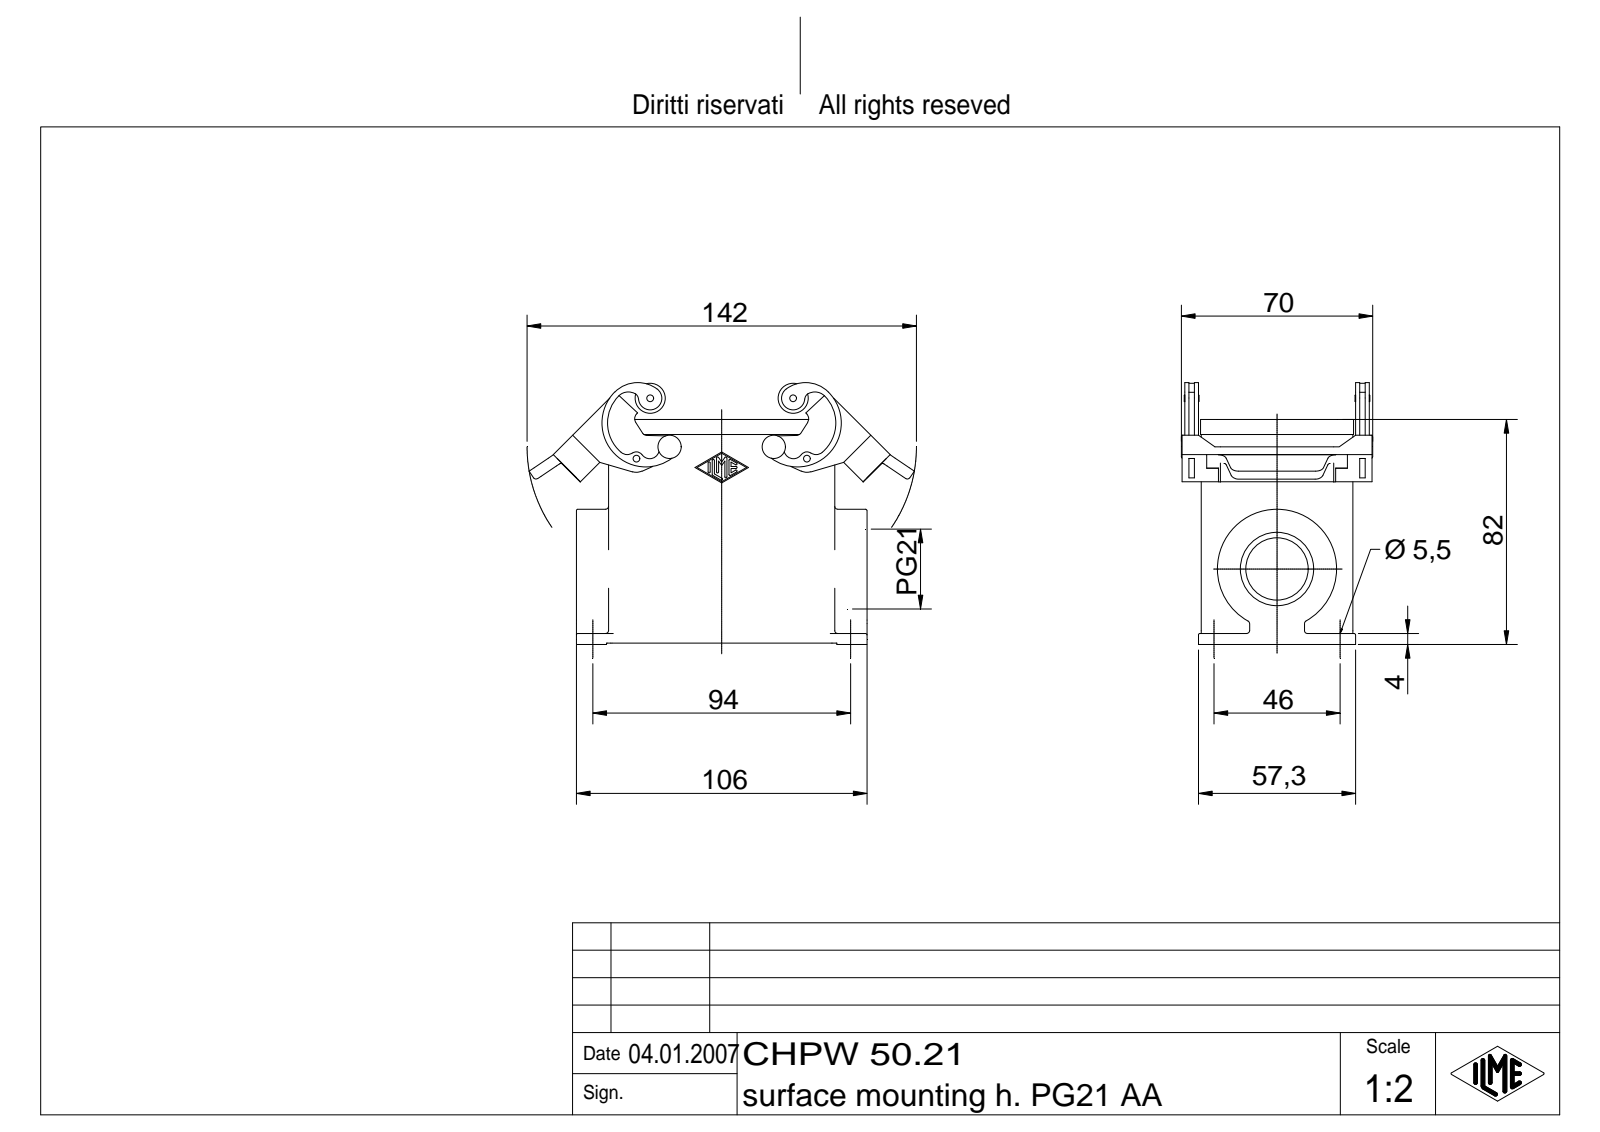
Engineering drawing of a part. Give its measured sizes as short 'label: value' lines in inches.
name: CHPW 50.21
written by: Autodesk Inventor 7 (AUTOMOTIVE_DESIGN)
unit: in
bodies: 1 solid, 911 faces (196 planar, 295 cylindrical, 420 other)
size: 5.531 × 3.757 × 2.748
volume: 9.922 in³; area: 118.4 in²
holes: 4× ⌀0.079, 4× ⌀0.097, 4× ⌀0.122, 2× ⌀0.098, 2× ⌀0.217, 1× ⌀0.897, 1× ⌀1.054
bosses: 2× ⌀0.433, 2× ⌀0.197, 2× ⌀0.118, 1× ⌀1.713
rounds: 30× R0.039, 14× R0.015, 14× R0.02, 12× R0.118, 8× R0.236, 6× R0.059, 6× R0.098, 4× R0.079
face distances: 0.118, 2.059, 2.177, 1.941, 0.138, 0.157, 0.433, 0.03, 3.13, 3.248
hole spacings: 0.63, 0.888, 2.411, 2.598, 2.674, 0.564, 0.929, 1.197
